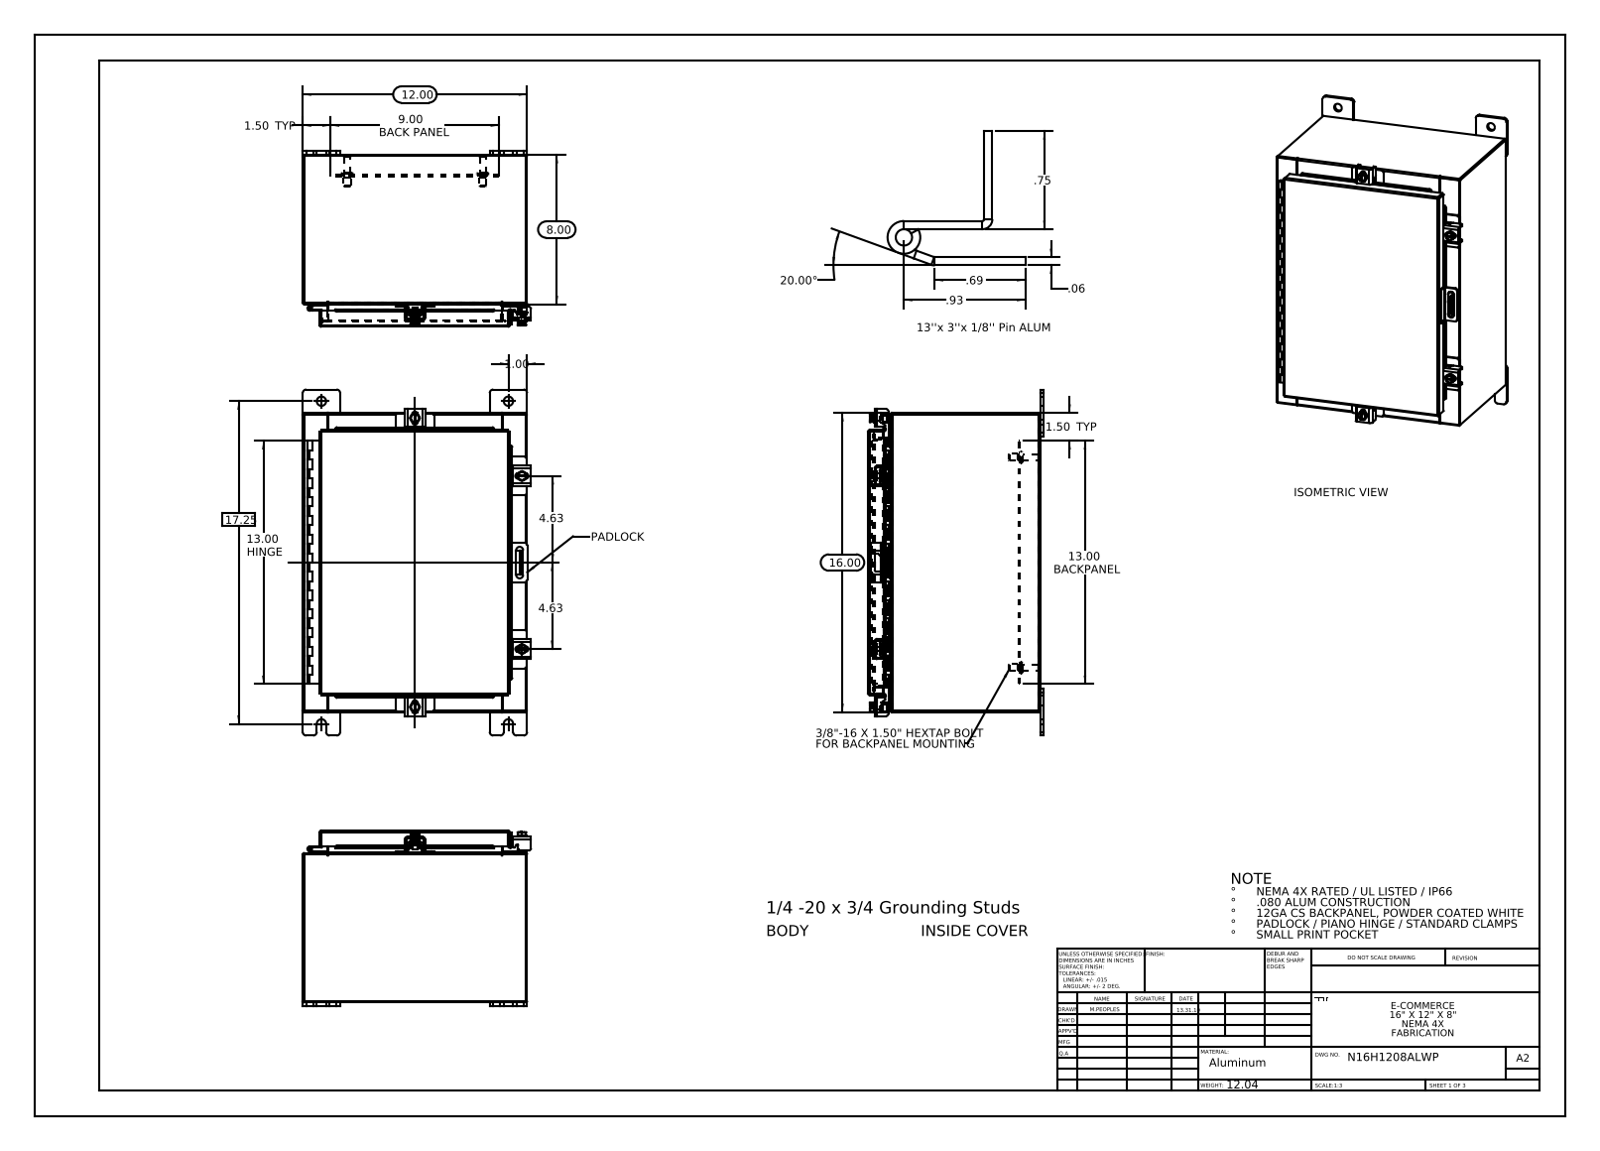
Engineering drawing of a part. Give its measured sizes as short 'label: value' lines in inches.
name: N16H1208ALWP 22104005_DEFAULT; N16H1208ALWP 22101002; N16H1208ALWP Clamp Bracket; N16H1208ALWP Padlock Staple (+8 more)
written by: SolidWorks 2013 (CONFIG_CONTROL_DESIGN)
unit: in
bodies: 37 solids, 1267 faces (680 planar, 507 cylindrical, 80 other)
size: 18.5 × 12.211 × 9.389
volume: 89.65 in³; area: 2 294 in²
holes: 8× ⌀0.5, 4× ⌀0.213, 4× ⌀0.26, 2× ⌀0.125, 1× ⌀0.125
bosses: 5× ⌀0.25, 4× ⌀0.625, 4× ⌀0.5, 4× ⌀0.399, 4× ⌀0.375, 4× ⌀0.33
rounds: 24× R0.19, 23× R0.013, 22× R0.06, 21× R0.088, 10× R0.125, 8× R0.12, 8× R0.141, 7× R0.05
face distances: 0.075, 9.126, 11.925, 15.925, 9.201, 9.051, 7.925, 1.201, 11.85, 12
hole spacings: 13.834, 2.225, 2.327, 3.3, 4.189, 4.19, 5.012, 5.08
